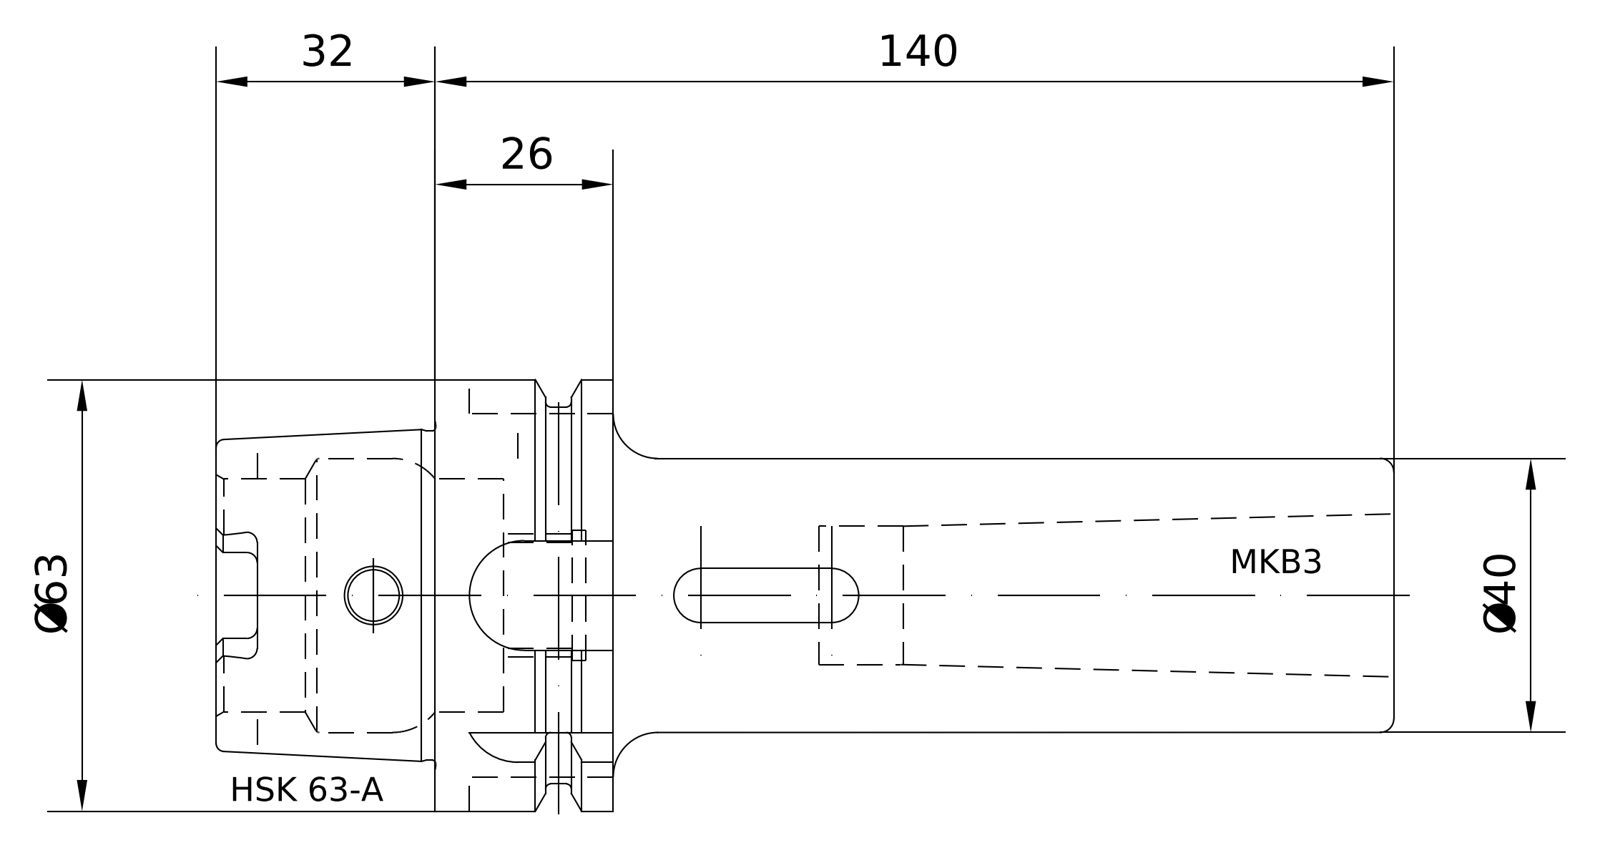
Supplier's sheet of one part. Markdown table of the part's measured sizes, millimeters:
| quantity | value |
| --- | --- |
| part name | A63-080-03 |
| STEP written by | PRO/ENGINEER BY PARAMETRIC TECHNOLOGY CORPORATION, 2010430 (CONFIG_CONTROL_DESIGN) |
| units | millimeters |
| bodies | 1 solid, 174 faces (58 planar, 48 cylindrical, 68 other) |
| overall size | 172 × 63 × 63 |
| volume | 194 764 mm³ |
| surface area | 42 075 mm² |
| round holes (diameter × count) | 7.5 × 1, 10 × 1, 16.92 × 1, 18.32 × 1, 18.66 × 1, 20.2 × 1, 34 × 1, 40 × 1 |
| round bosses / shafts (diameter × count) | 63 × 1, 55 × 1, 48.04 × 1, 18 × 1 |
| partial cylindrical surfaces (radius × count) | 1.5 × 6, 3 × 4, 8 × 1, 8.02 × 1, 9.02 × 1 |
| main face-to-face distances | 26, 140, 114, 10, 16, 130, 32, 42, 58, 172 |
